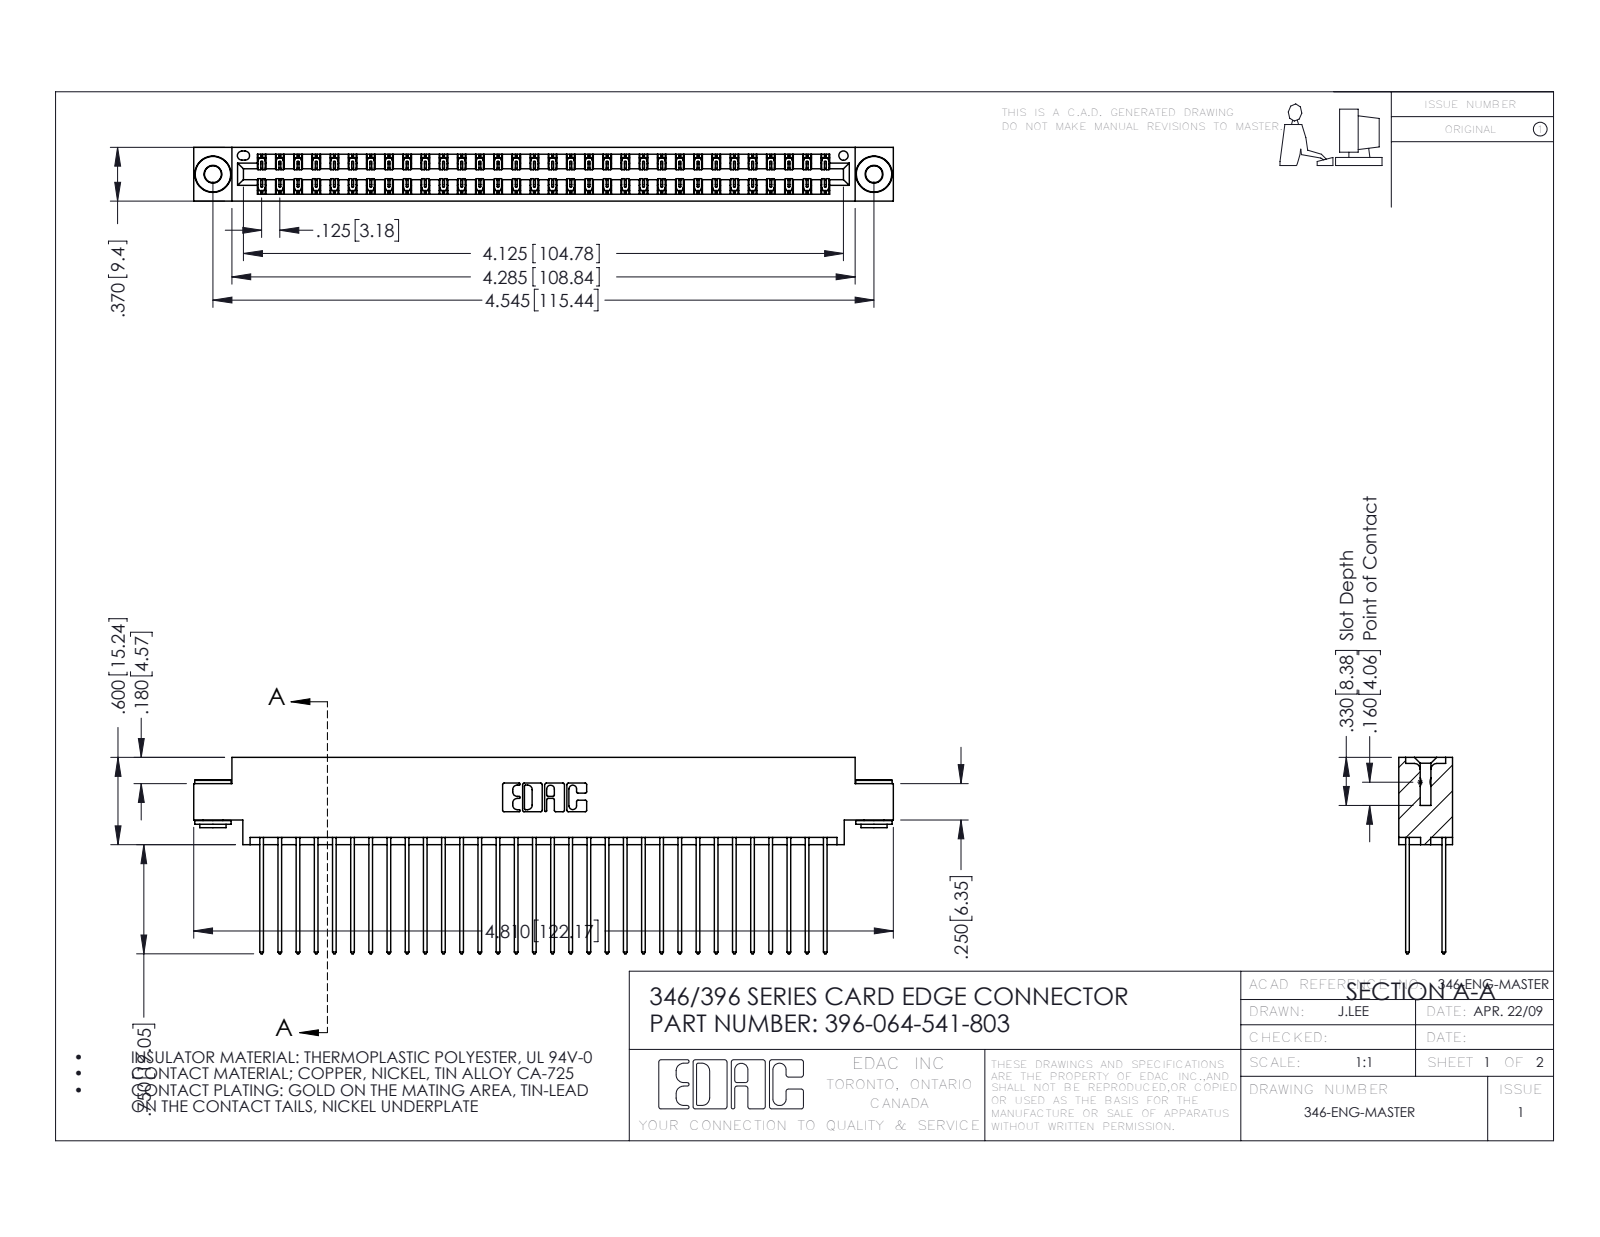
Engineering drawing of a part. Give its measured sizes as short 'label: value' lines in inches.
name: 345-250-002_345-250-002-102; 346 Part_0.170 Offset - 0.156 Dia-TH; 396-064-541-803; 345-292-001_345-293-141
written by: SolidWorks 2016 (CONFIG_CONTROL_DESIGN)
unit: in
bodies: 67 solids, 3492 faces (2330 planar, 1154 cylindrical, 8 other)
size: 4.81 × 1.35 × 0.37
volume: 0.736 in³; area: 28.81 in²
holes: 2× ⌀0.116, 2× ⌀0.156, 1× ⌀0.064
bosses: 2× ⌀0.25, 2× ⌀0.18, 2× ⌀0.136
rounds: 96× R0.006, 64× R0.01, 22× R0.01, 6× R0.007, 6× R0.031, 3× R0.026, 2× R0.014, 2× R0.022
face distances: 0.048, 0.322, 0.25, 0.025, 0.072, 0.298, 0.37, 0.275, 0.225, 0.148
hole spacings: 0.246, 4.337, 4.545
